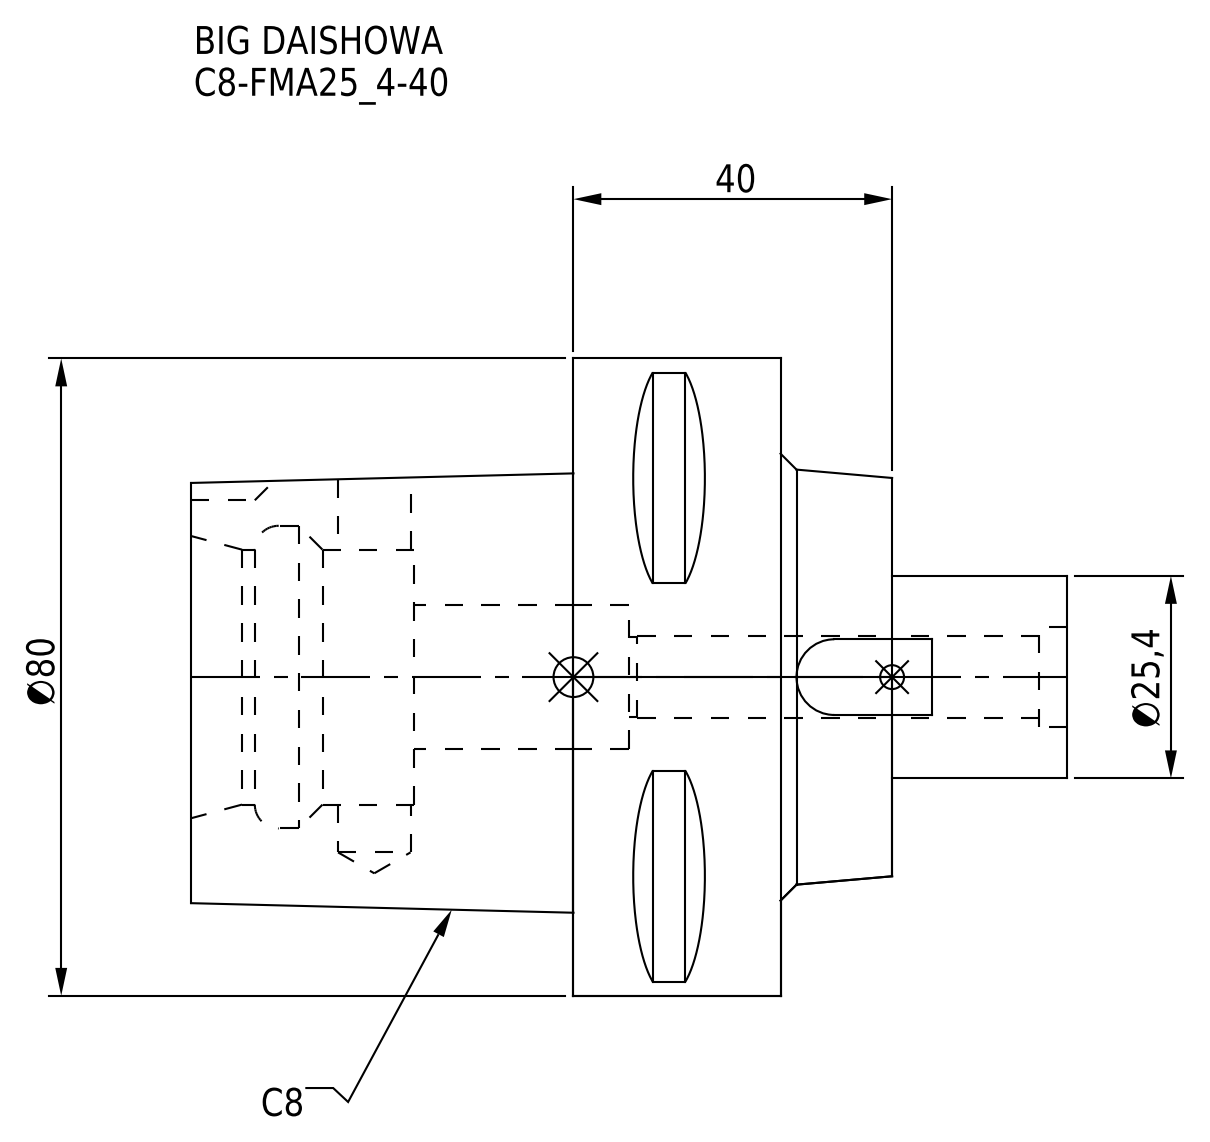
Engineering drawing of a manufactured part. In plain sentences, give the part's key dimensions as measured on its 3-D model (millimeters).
The part is named "C8-FMA25_4-40". Its 3-D file was written by "CREO PARAMETRIC BY PTC INC, 2016380 (AUTOMOTIVE_DESIGN)". It is 1 solid with 78 faces: 41 planar, 23 cylindrical and 14 other. Overall it measures 110 by 80 by 80 millimeters. Its volume is 239 757 cubic millimeters and its surface area 35 743 square millimeters. Round holes: 1 of diameter 9.1, 1 of diameter 10, 1 of diameter 10.25, 1 of diameter 12.5, 1 of diameter 18, 1 of diameter 32, 1 of diameter 38. Round bosses or shafts: 1 of diameter 80, 1 of diameter 25.4. Partial cylindrical surfaces (rounded edges, fillets, slot ends): 1 of radius 6. The main face-to-face distances are 26, 40, 14, 48, 88, 74, 20, 28, 60, 46.
